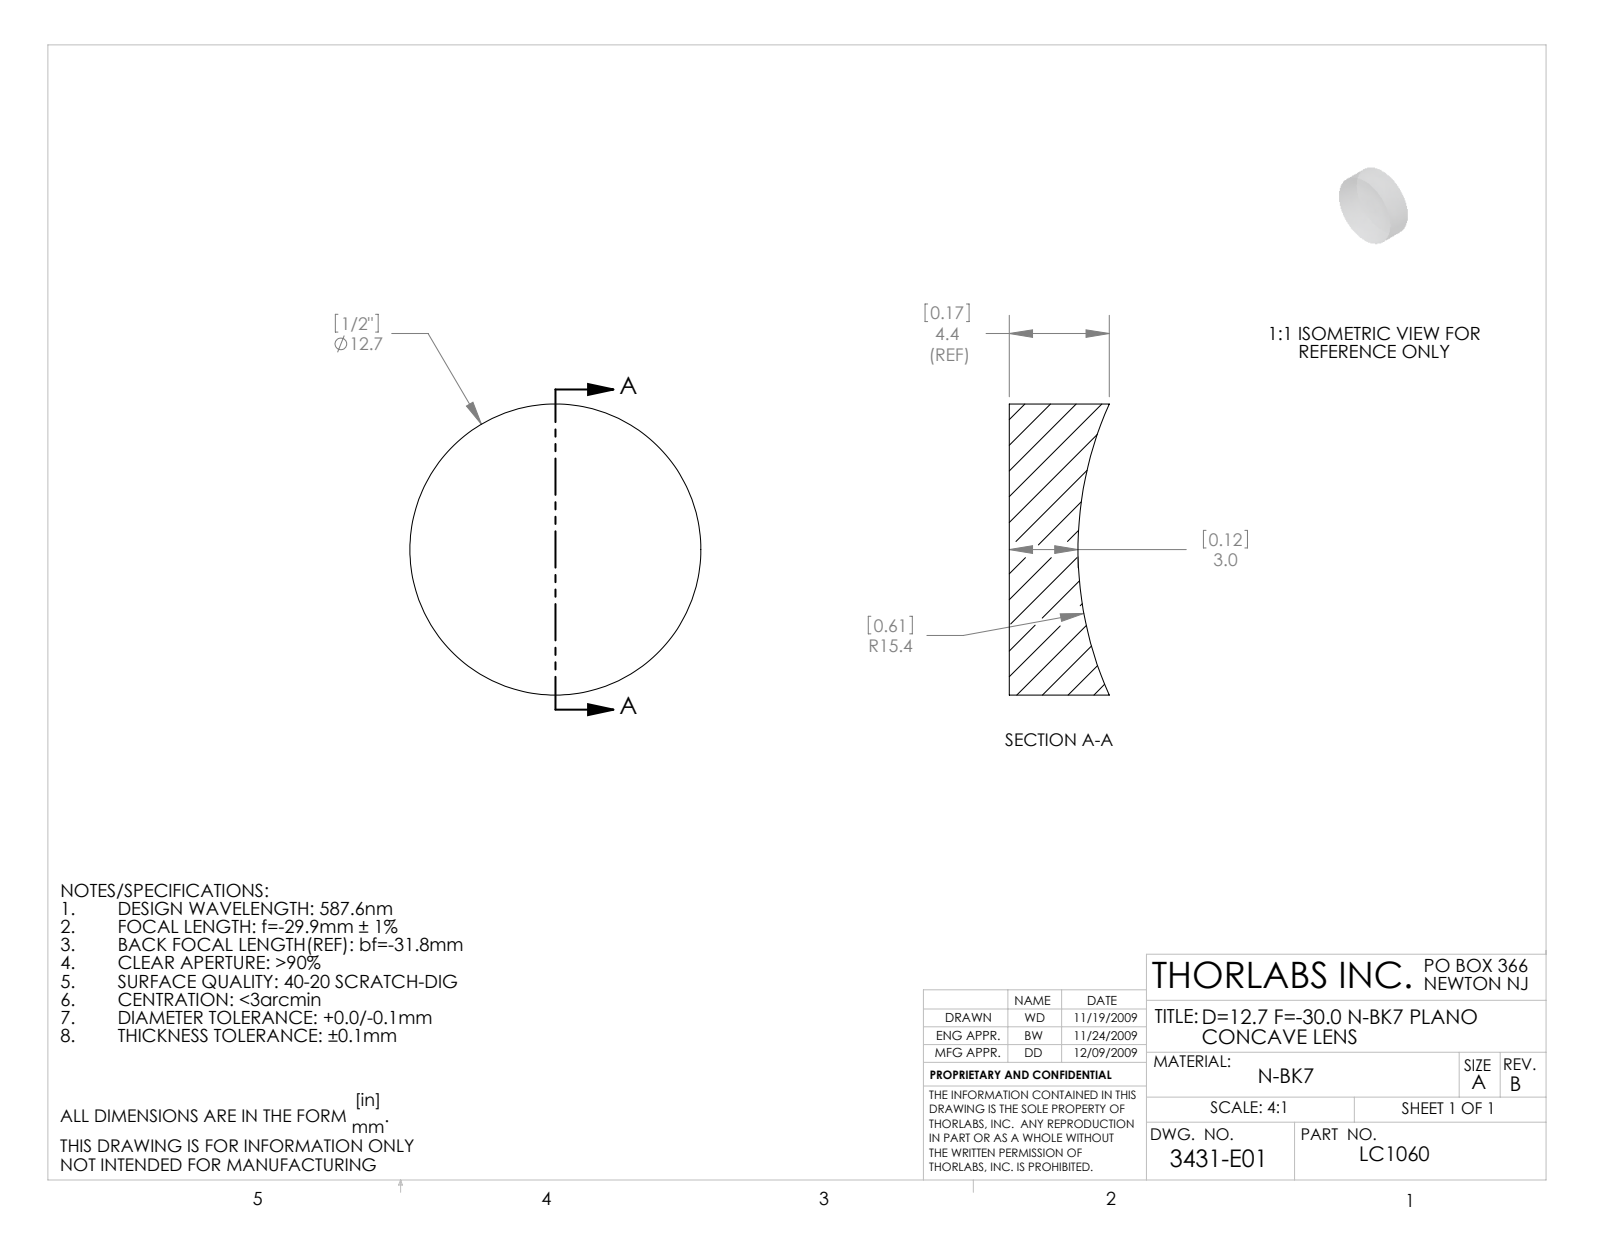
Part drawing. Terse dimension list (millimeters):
name: 3431-E0W
written by: SolidWorks 2009 (AUTOMOTIVE_DESIGN)
unit: mm
bodies: 1 solid, 5 faces (1 planar, 2 cylindrical, 2 other)
size: 12.7 × 12.7 × 4.37
volume: 465 mm³; area: 433 mm²
bosses: 1× ⌀12.7
